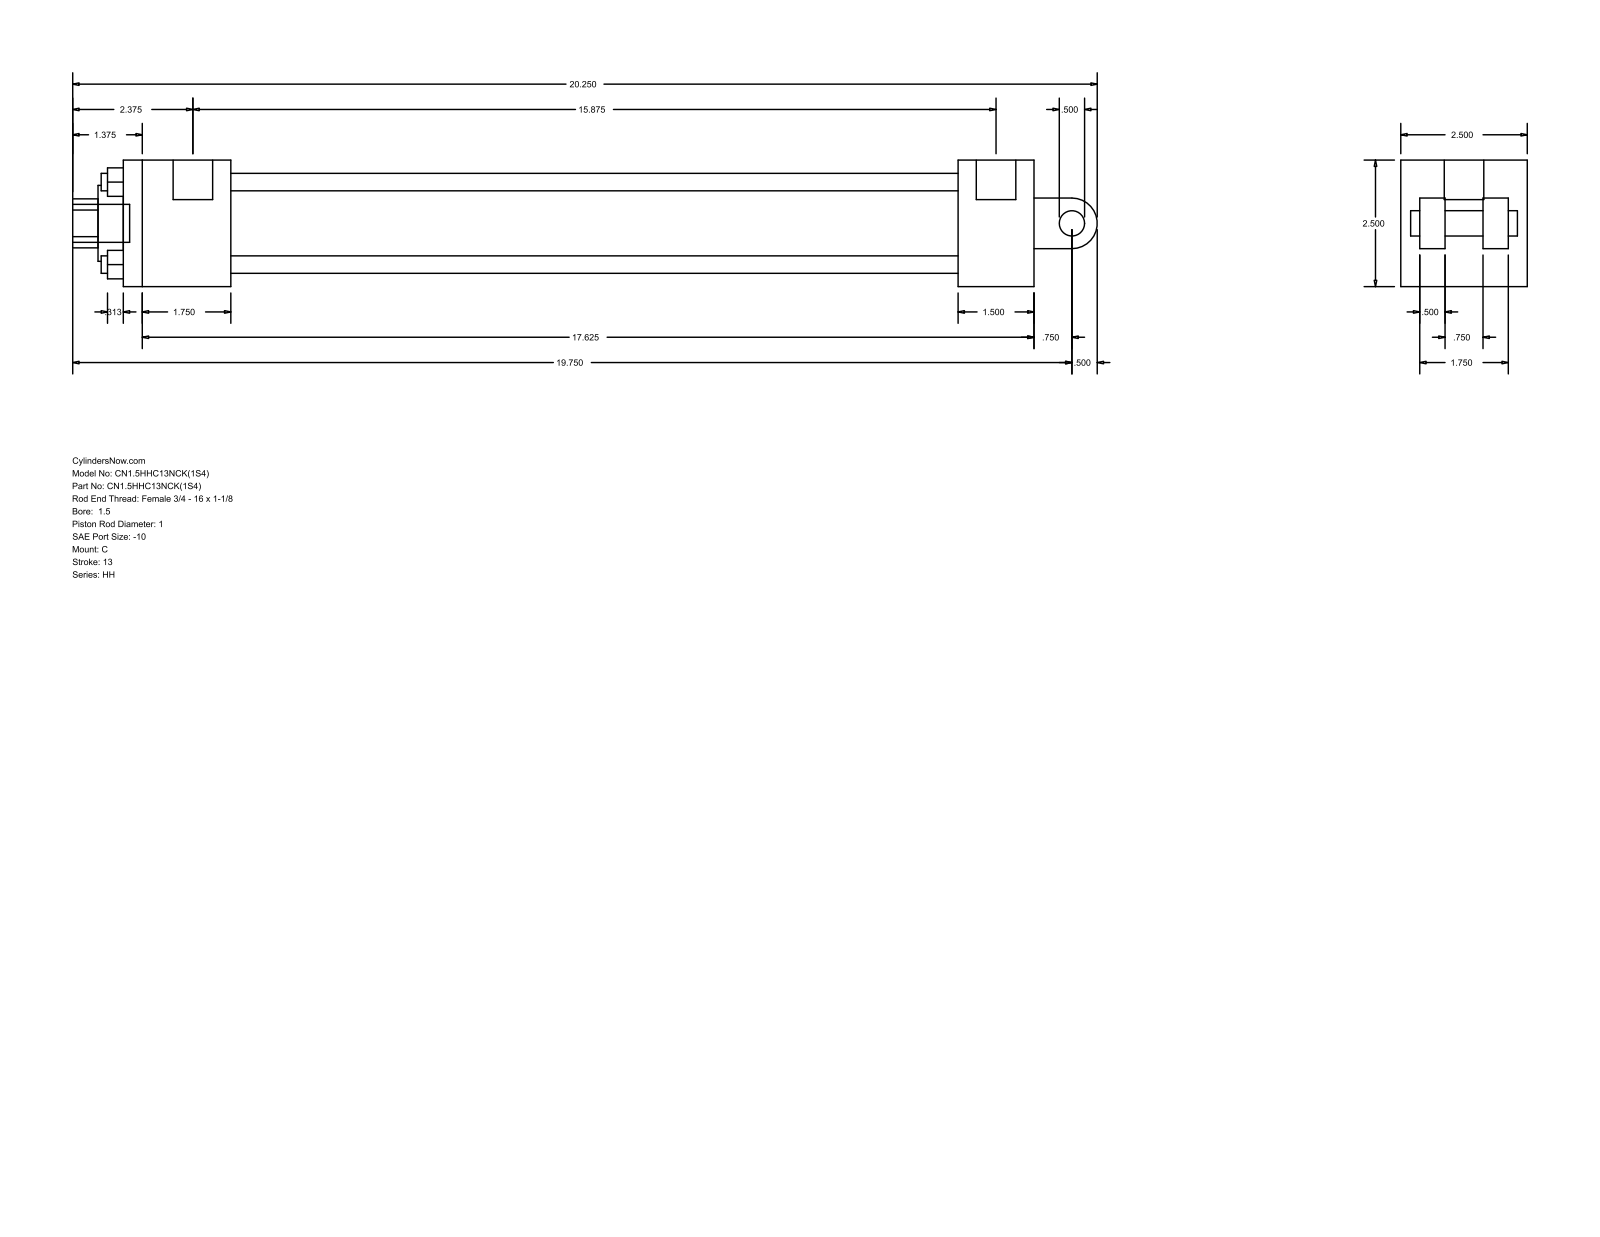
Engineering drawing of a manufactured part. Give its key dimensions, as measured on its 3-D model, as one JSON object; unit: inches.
{"part_name": "HH_C__0150_1", "step_written_by": "GSSL Pune (CONFIG_CONTROL_DESIGN)", "units": "inches", "bodies": {"solids": 0, "faces": 99, "planar": 70, "cylindrical": 29, "other": 0}, "overall_size": [20.25, 2.5, 2.5], "round_holes": [[0.345, 4], [0.219, 2], [0.781, 1], [1, 1], [1.5, 1], [1.75, 1]], "round_bosses_or_shafts": [[0.219, 2], [0.781, 1], [0.75, 1], [0.5, 1]], "partial_cylinders_radius": [[0.484, 1], [0.5, 1]], "face_to_face_distances": [2.5, 2.125, 14.375, 15.875, 1.5, 16.5, 18, 0.5, 0.375, 0.875], "hole_center_spacings": [1.152, 1.63, 2.305, 0.063]}
